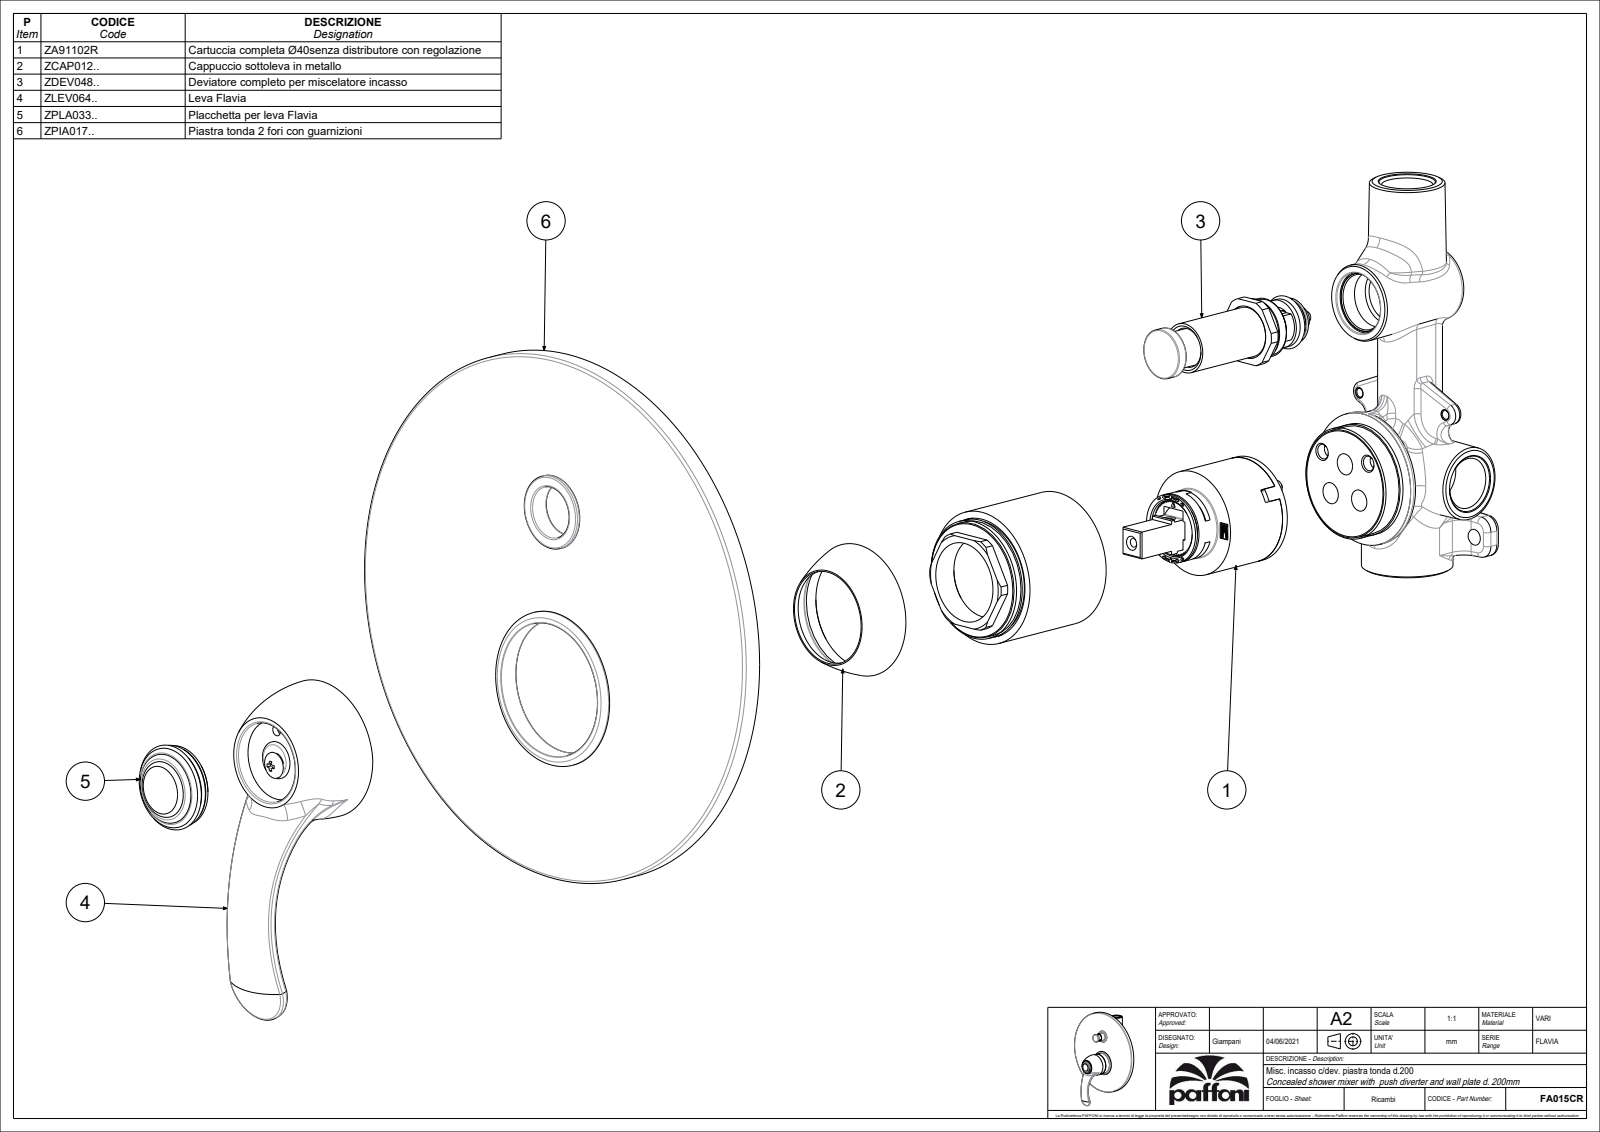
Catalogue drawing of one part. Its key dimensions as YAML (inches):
part_name: "FA015CR"
step_written_by: "CREO PARAMETRIC BY PTC INC, 2020044 (CONFIG_CONTROL_DESIGN)"
units: inches
bodies: {solids: 2, faces: 150, planar: 37, cylindrical: 36, other: 77}
overall_size: [8.854, 7.874, 3.017]
volume: 18.74
surface_area: 151
round_holes:
  - {diameter: 0.157, count: 1}
  - {diameter: 0.276, count: 1}
  - {diameter: 1.181, count: 1}
  - {diameter: 1.378, count: 1}
  - {diameter: 1.713, count: 1}
  - {diameter: 1.772, count: 1}
round_bosses_or_shafts:
  - {diameter: 7.874, count: 1}
  - {diameter: 2.303, count: 1}
  - {diameter: 1.98, count: 1}
  - {diameter: 1.177, count: 1}
  - {diameter: 1.091, count: 1}
  - {diameter: 1.063, count: 1}
  - {diameter: 0.736, count: 1}
  - {diameter: 0.732, count: 1}
partial_cylinders:
  - {radius: 0.059, count: 4}
face_to_face_distances: [0.315, 0.098, 0.413, 1.894, 2.209, 1.795, 0.02, 2.307, 1.913, 1.992]
hole_center_spacings: [0.058, 0.064, 0.448, 0.454, 0.512]
